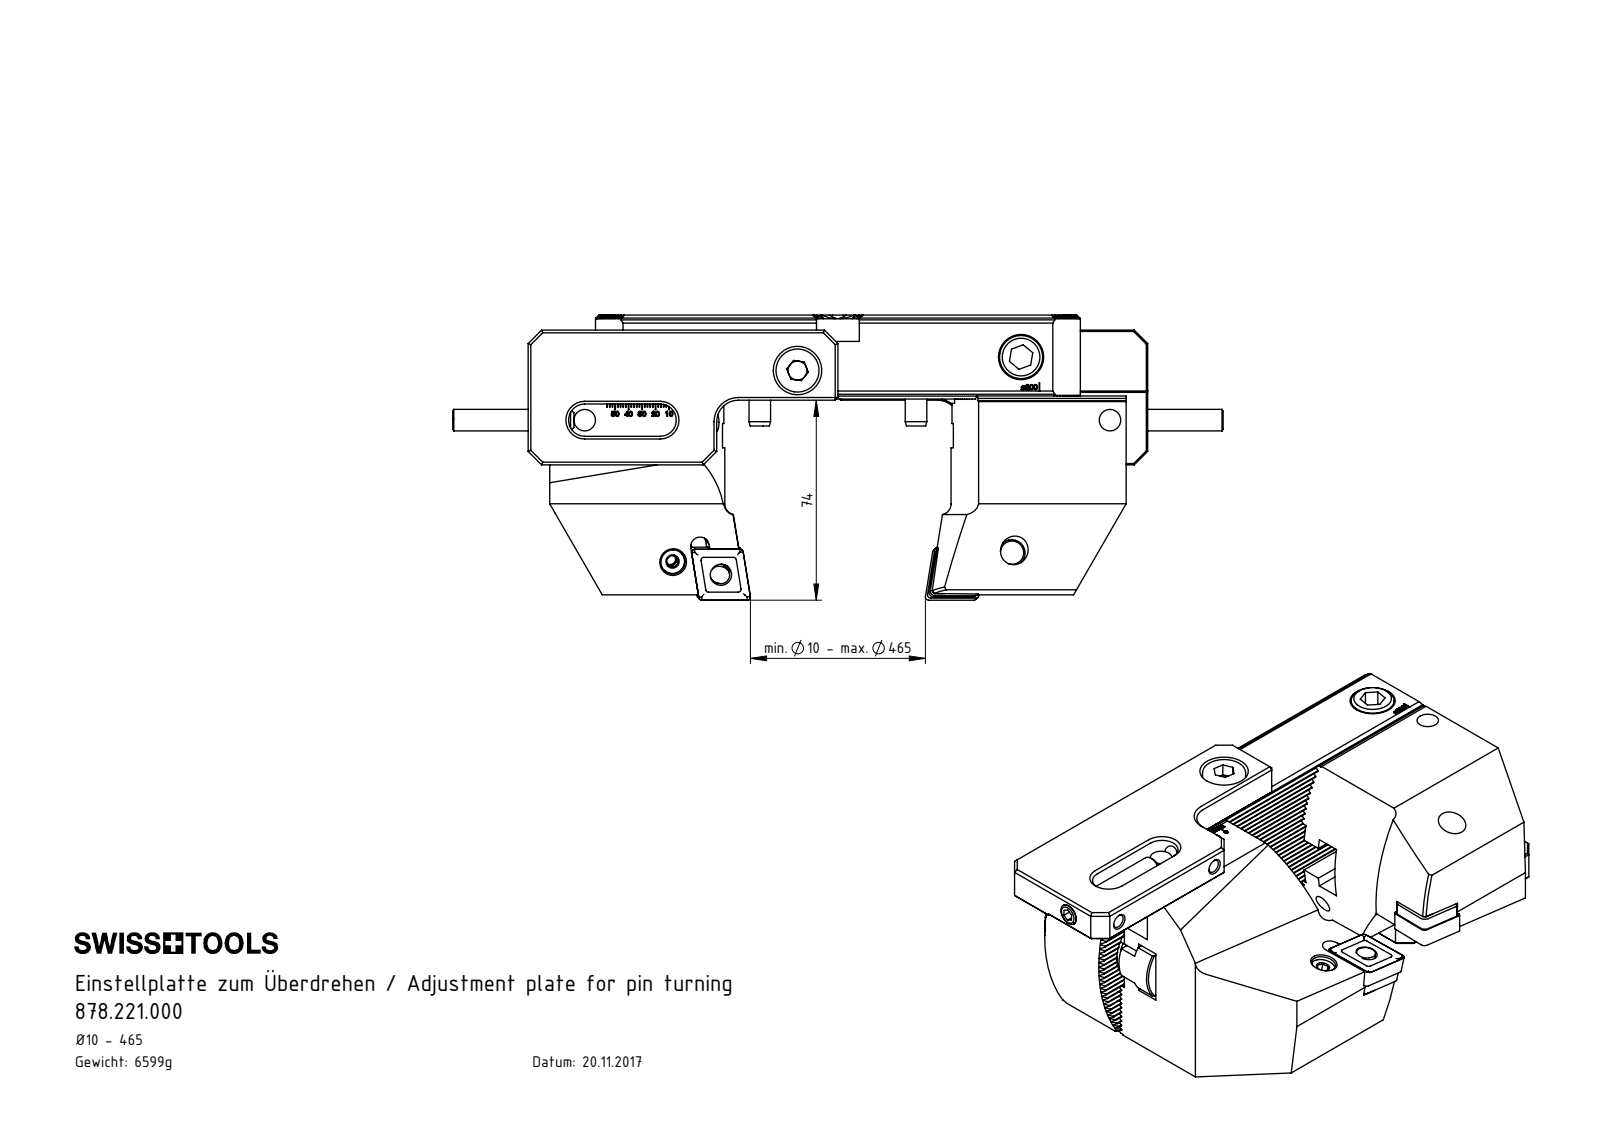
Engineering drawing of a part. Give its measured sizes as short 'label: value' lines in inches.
name: VK1-ER7.002.012_C; ISO 8734 - 6 x 14; DIN 7984 - M10 x 16; ISO 4026 - M8 x 45 (+1 more)
written by: SolidWorks 2017 (AUTOMOTIVE_DESIGN)
unit: in
bodies: 5 solids, 109 faces (74 planar, 16 cylindrical, 19 other)
size: 4.972 × 1.969 × 0.866
volume: 3.055 in³; area: 27.22 in²
holes: 2× ⌀0.197, 2× ⌀0.236, 1× ⌀0.268, 1× ⌀0.433, 1× ⌀0.709
bosses: 1× ⌀0.63, 1× ⌀0.394, 1× ⌀0.315
rounds: 2× R0.236, 1× R0.315
face distances: 0.472, 0.02, 0.453, 1.969, 0.236, 1.024, 0.945, 0.217, 1.079, 0.055
hole spacings: 0.311, 0.73, 0.772, 1.969
